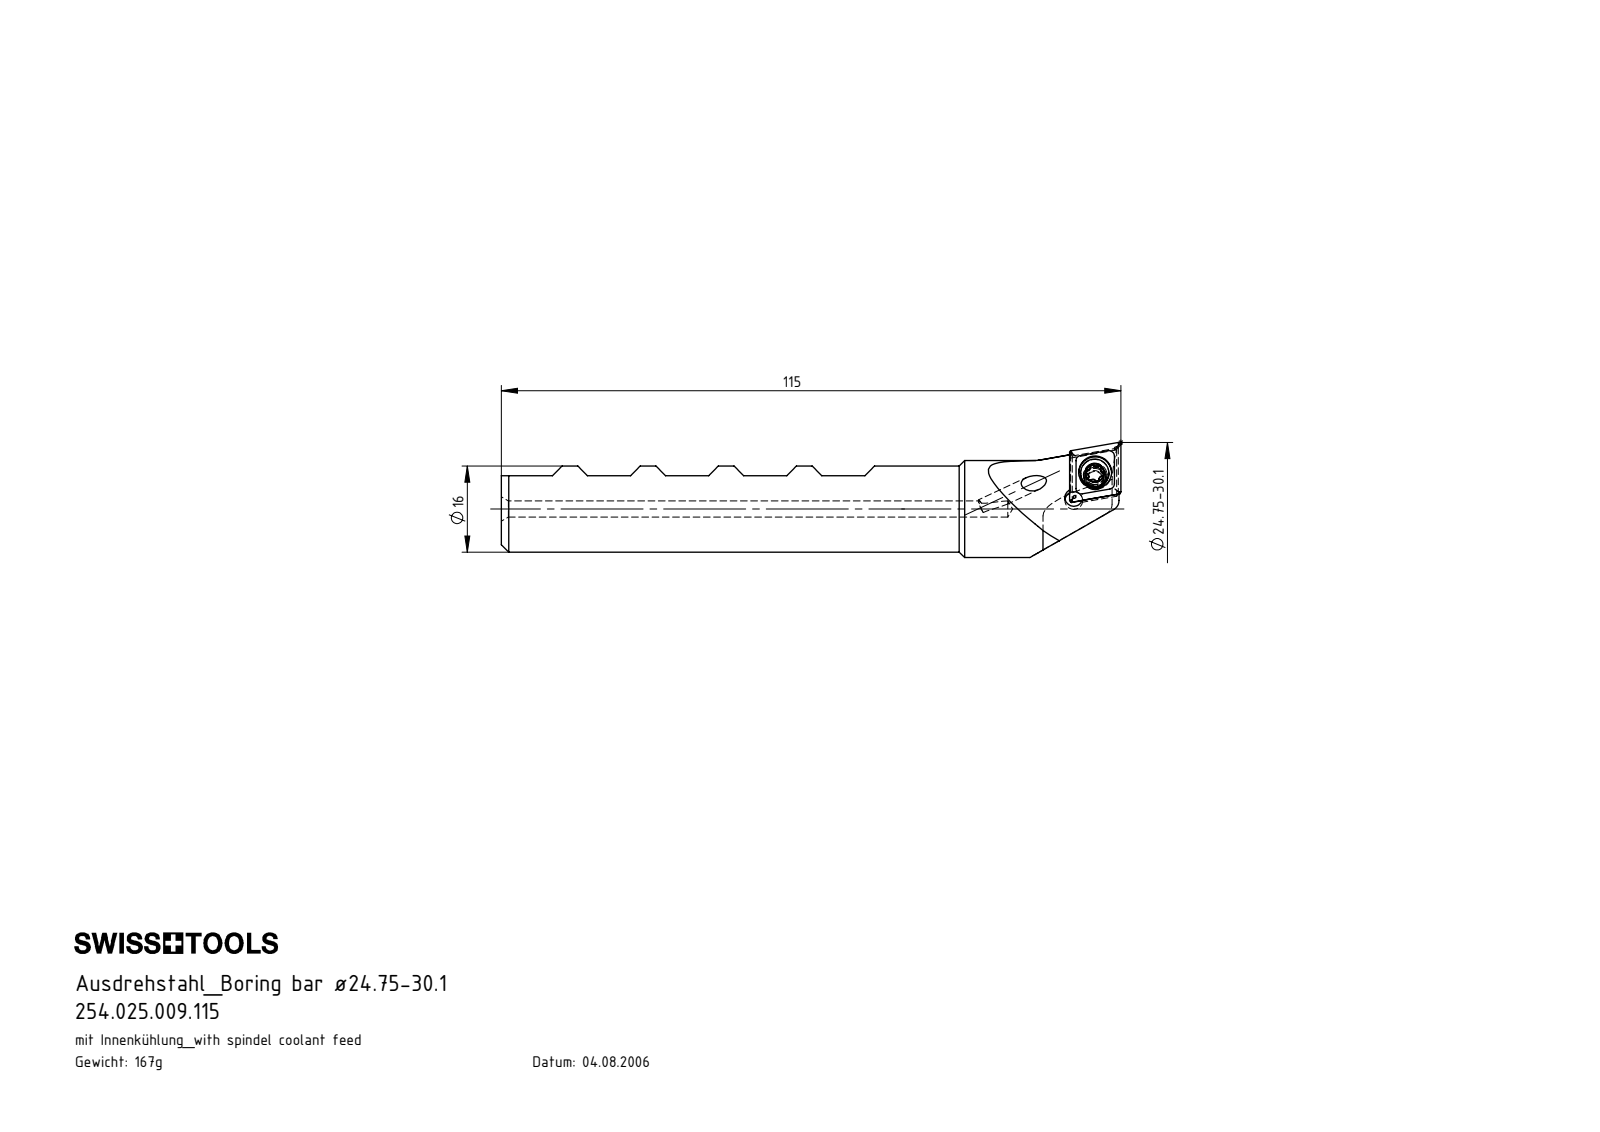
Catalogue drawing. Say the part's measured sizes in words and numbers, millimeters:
The part is named "CCMT09T304; WCB-ER2.001.009_A; B25-WCB.K11.115_B; 254.025.009.115". Its 3-D file was written by "SolidWorks 2017 (CONFIG_CONTROL_DESIGN)". It is 3 solids with 145 faces: 45 planar, 39 cylindrical and 61 other. Overall it measures 115 by 21.38 by 19.06 millimeters. Its volume is 21 236 cubic millimeters and its surface area 7 608 square millimeters. Round holes: 2 of diameter 3, 2 of diameter 3.3, 1 of diameter 4.4, 1 of diameter 6.1. Round bosses or shafts: 1 of diameter 18, 1 of diameter 16, 1 of diameter 5.25, 1 of diameter 4. Partial cylindrical surfaces (rounded edges, fillets, slot ends): 6 of radius 0.34, 6 of radius 0.59, 1 of radius 2, 1 of radius 9.2, 1 of radius 12. The main face-to-face distances are 10.25, 6.95, 20.5, 20.51, 30.76, 10.72, 3.77, 10.92, 3.97, 30.75. The hole center spacings are 6.07, 6.19.
